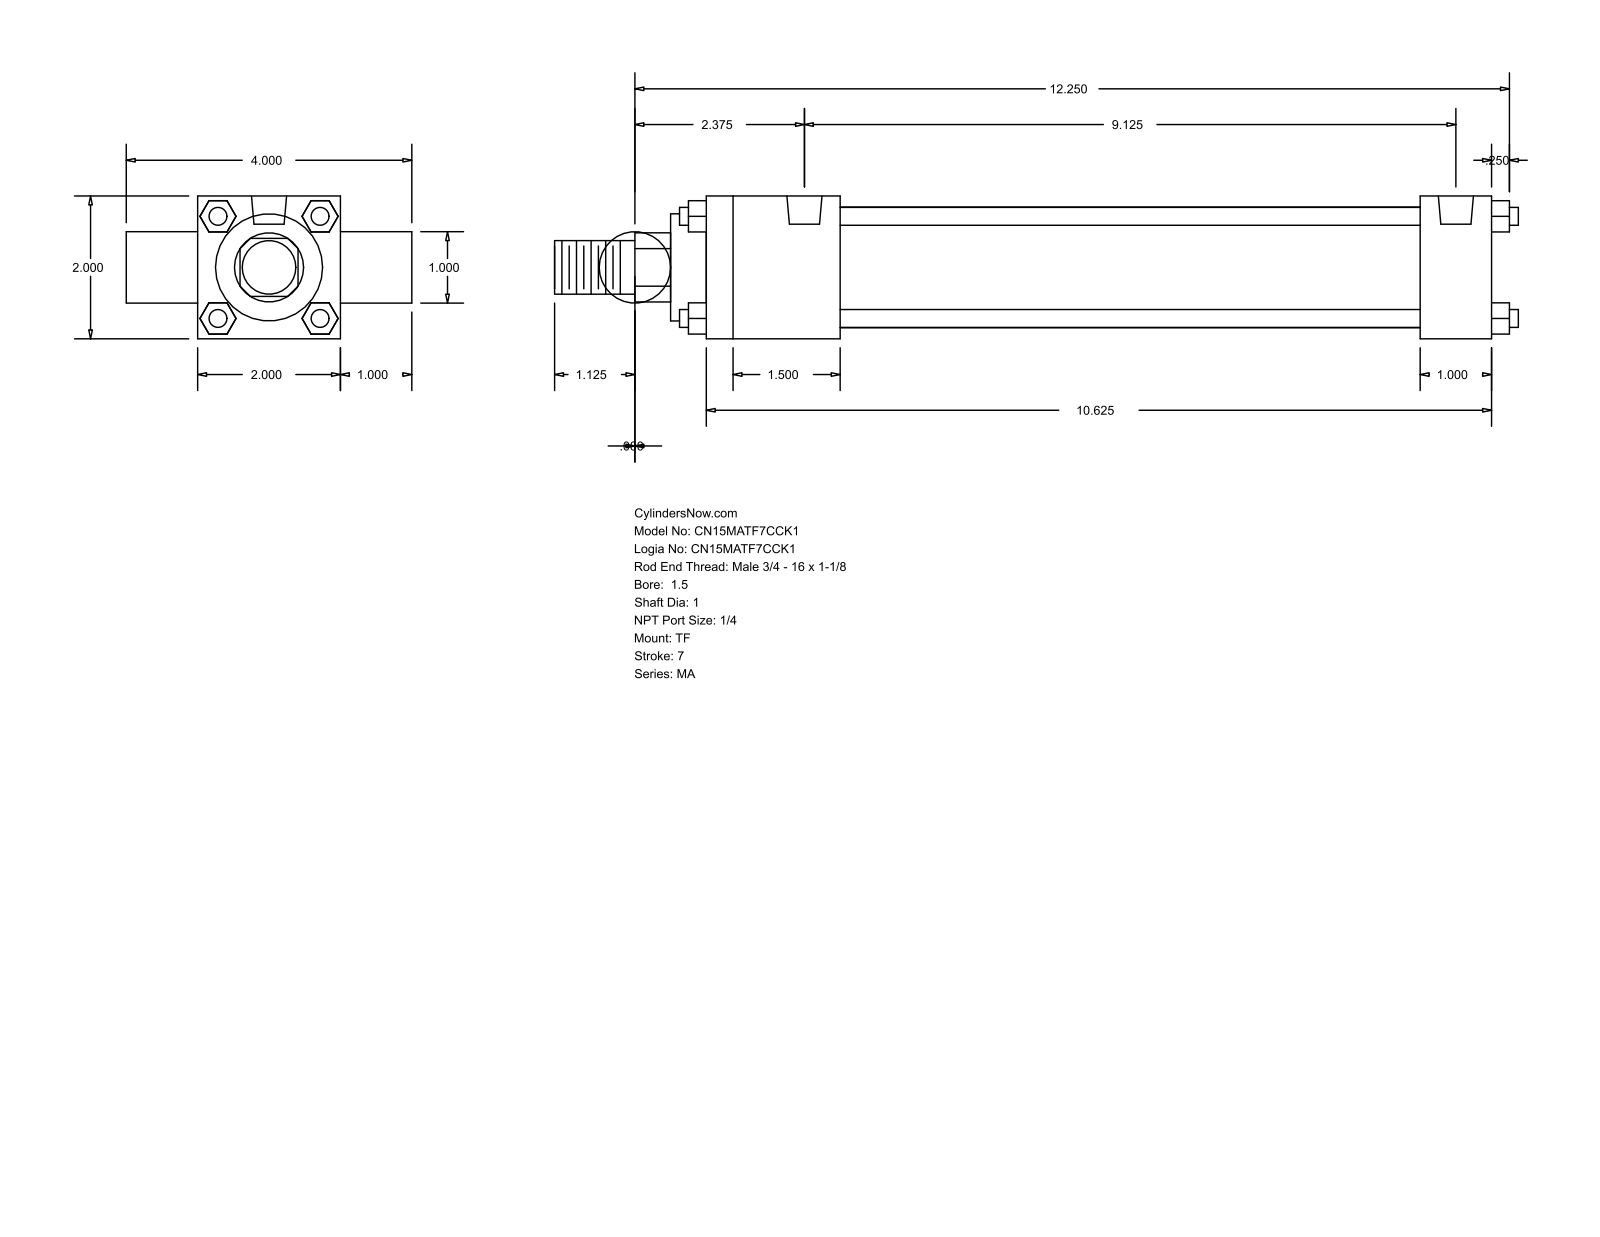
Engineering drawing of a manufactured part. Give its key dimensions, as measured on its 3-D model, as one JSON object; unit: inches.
{"part_name": "MA_TF__0150_1", "step_written_by": "GSSL Pune (CONFIG_CONTROL_DESIGN)", "units": "inches", "bodies": {"solids": 0, "faces": 120, "planar": 92, "cylindrical": 28, "other": 0}, "overall_size": [13.5, 4, 2], "round_holes": [[0.313, 3], [0.492, 2]], "round_bosses_or_shafts": [[0.25, 4], [1, 2], [1.69, 1], [1.5, 1], [0.75, 1]], "partial_cylinders_radius": [[0.484, 1]], "face_to_face_distances": [2, 1, 11, 3, 0.25, 1.875, 10, 8.125, 9.125, 11.5], "hole_center_spacings": [9.125]}
